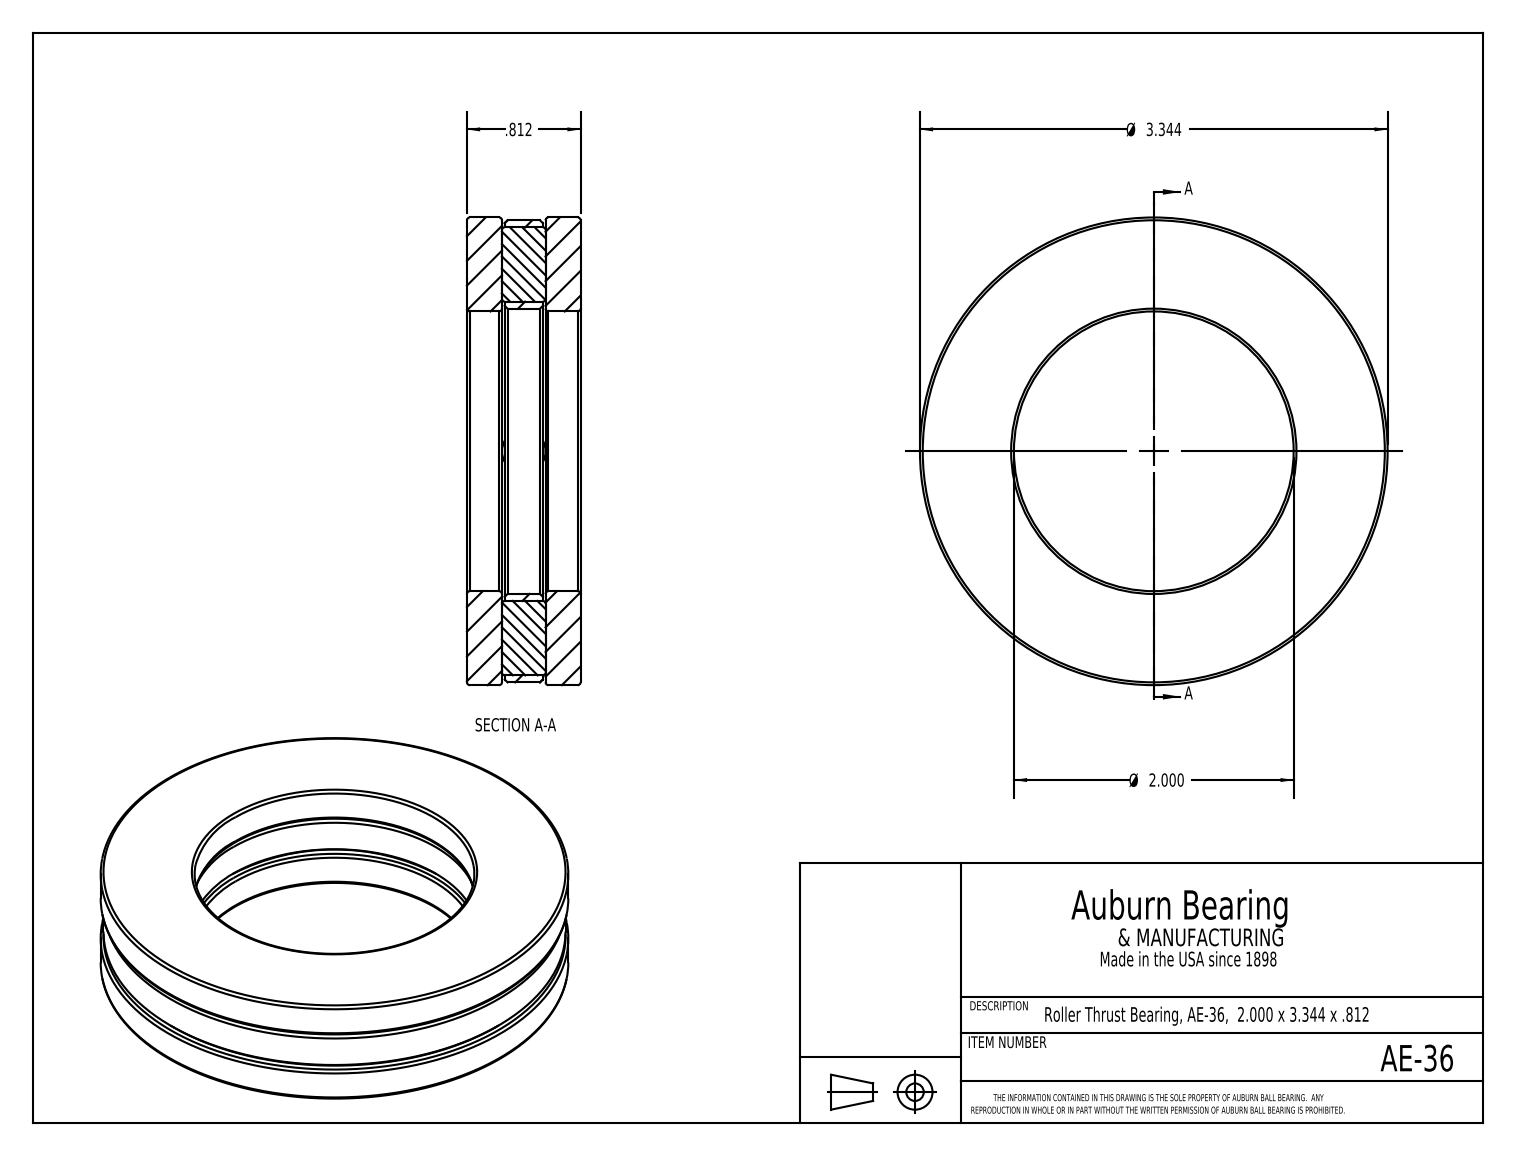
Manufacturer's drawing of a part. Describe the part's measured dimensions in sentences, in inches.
The part is named "AE-36". Its 3-D file was written by "SolidWorks 2017 (CONFIG_CONTROL_DESIGN)". It is 7 solids with 60 faces: 30 planar, 10 cylindrical and 20 other. Overall it measures 3.344 by 3.344 by 0.812 inches. Its volume is 4.231 cubic inches and its surface area 48.29 square inches. Round holes: 1 of diameter 2, 1 of diameter 2.04. Round bosses or shafts: 2 of diameter 0.312, 1 of diameter 3.344, 1 of diameter 3.304. The main face-to-face distances are 0.25, 0.562, 0.27, 0.542, 0.02, 0.292, 0.312, 0.812, 0.272, 0.914.
